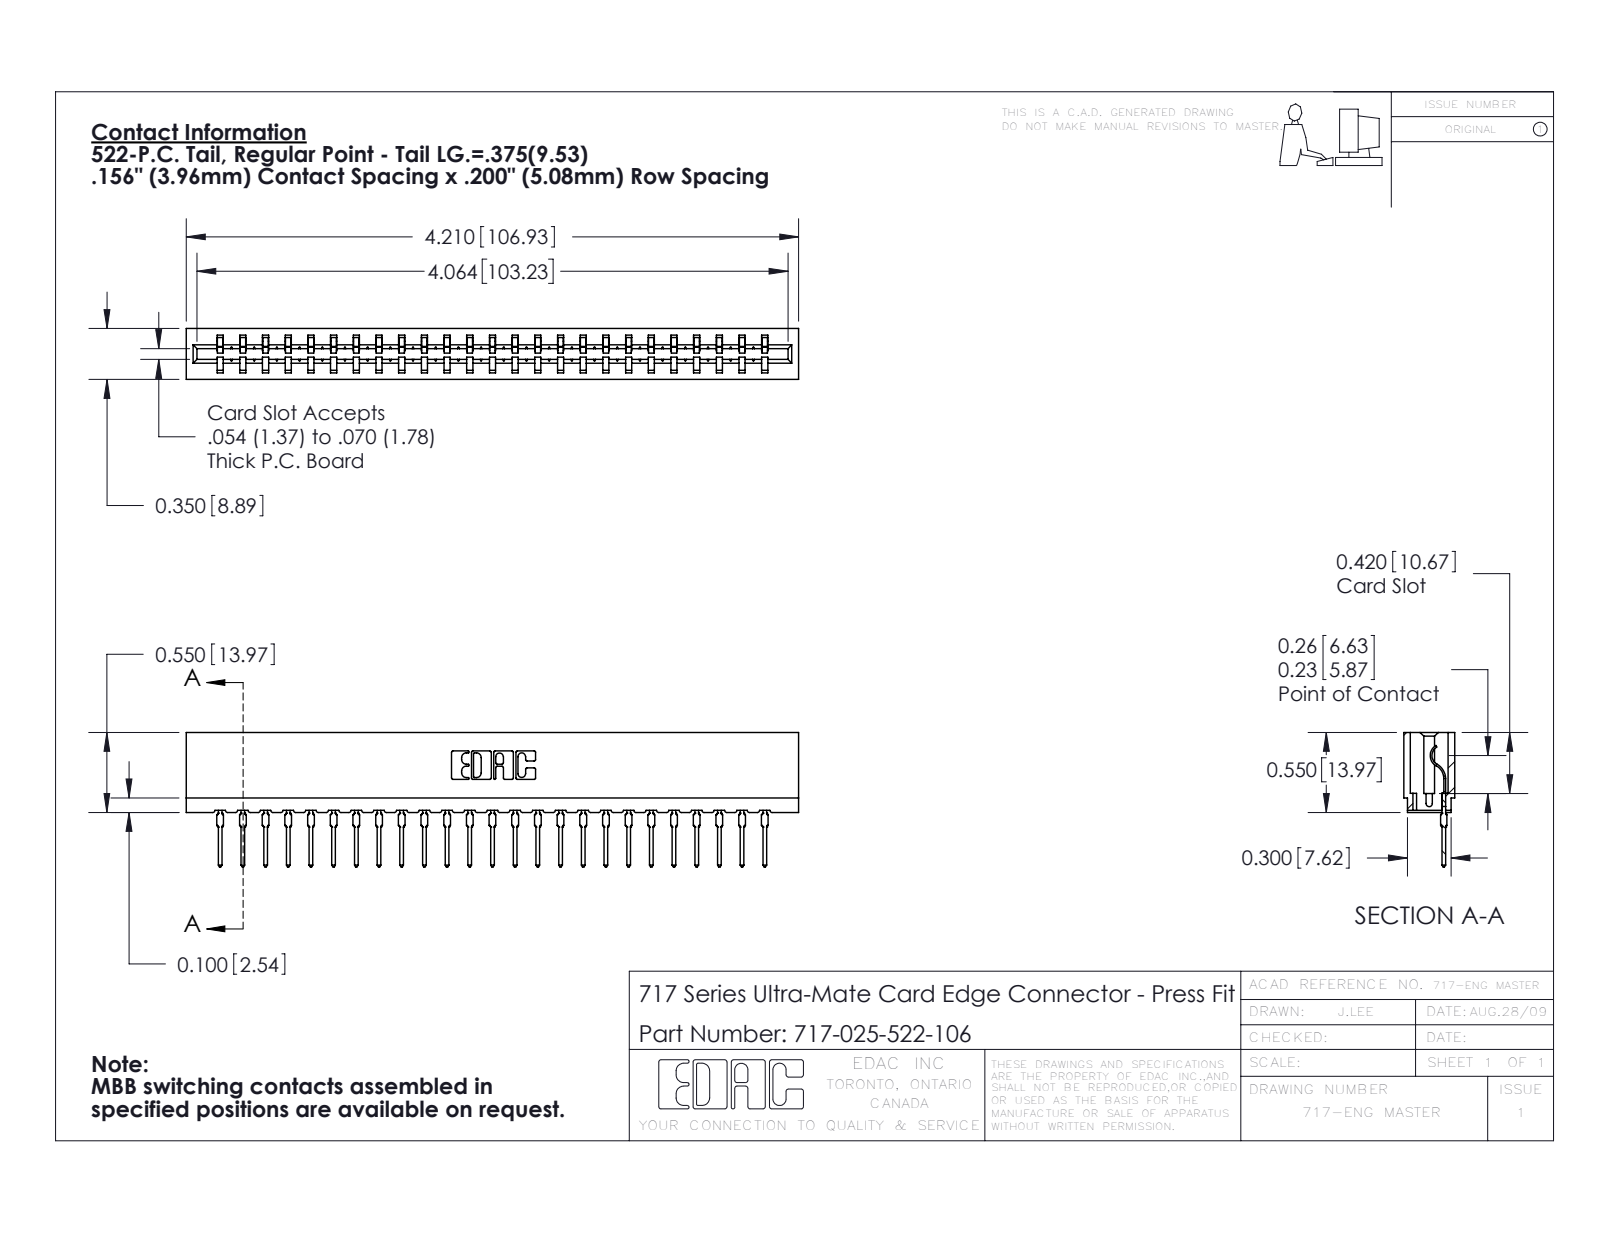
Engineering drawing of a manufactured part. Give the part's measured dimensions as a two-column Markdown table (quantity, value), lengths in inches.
| quantity | value |
| --- | --- |
| part name | 717 Part_Insulator Option - 06; 717-025-522-106; 745-292-001_522 |
| STEP written by | SolidWorks 2016 (CONFIG_CONTROL_DESIGN) |
| units | inches |
| bodies | 26 solids, 2919 faces (1754 planar, 515 cylindrical, 650 other) |
| overall size | 4.21 × 0.924 × 0.35 |
| volume | 0.556 in³ |
| surface area | 19.65 in² |
| partial cylindrical surfaces (radius × count) | 0.015 × 50, 0.021 × 50, 0.01 × 22, 0.007 × 6, 0.031 × 6, 0.005 × 4, 0.011 × 4, 0.026 × 3 |
| main face-to-face distances | 0.212, 0.138, 0.35, 0.156, 0.074, 0.624, 0.045, 0.305, 0.093, 0.167 |
